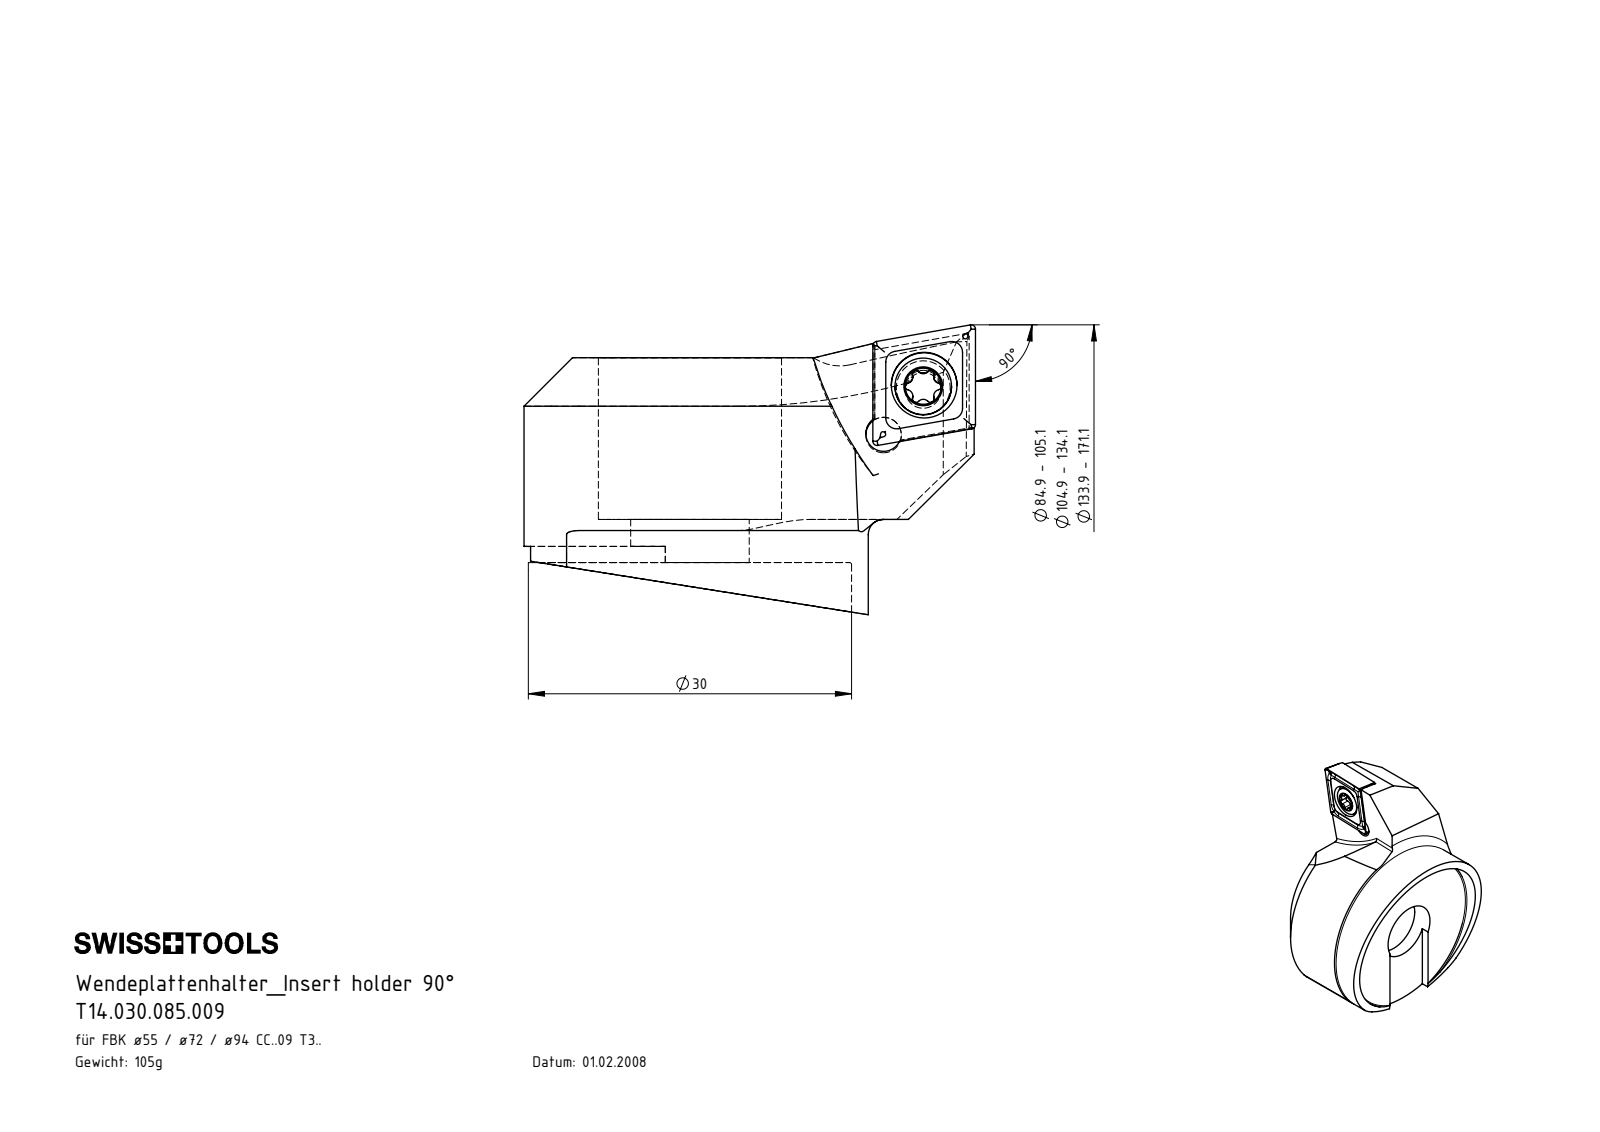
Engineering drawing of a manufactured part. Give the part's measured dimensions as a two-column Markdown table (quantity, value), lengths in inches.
| quantity | value |
| --- | --- |
| part name | F55.WCB.001.022; WCB-ER2.001.009_A; F55-WCB.001.022_D_fertigbearbeitet; CCMT09T304 |
| STEP written by | SolidWorks 2017 (AUTOMOTIVE_DESIGN) |
| units | inches |
| bodies | 3 solids, 120 faces (41 planar, 31 cylindrical, 48 other) |
| overall size | 1.65 × 1.307 × 1.059 |
| volume | 0.813 in³ |
| surface area | 8.759 in² |
| round holes (diameter × count) | 0.13 × 2, 0.173 × 1, 0.24 × 1, 0.433 × 1, 0.669 × 1, 1.181 × 1 |
| round bosses / shafts (diameter × count) | 0.207 × 1, 0.157 × 1 |
| partial cylindrical surfaces (radius × count) | 0.013 × 6, 0.023 × 6, 0.02 × 2, 0.394 × 2, 0.197 × 1, 0.652 × 1, 0.654 × 1, 0.823 × 1 |
| main face-to-face distances | 0.748, 0.591, 0.157, 0.689, 0.098, 0.059, 0.148, 0.156, 0.394, 0.354 |
| hole center spacings | 0.226, 0.231 |
